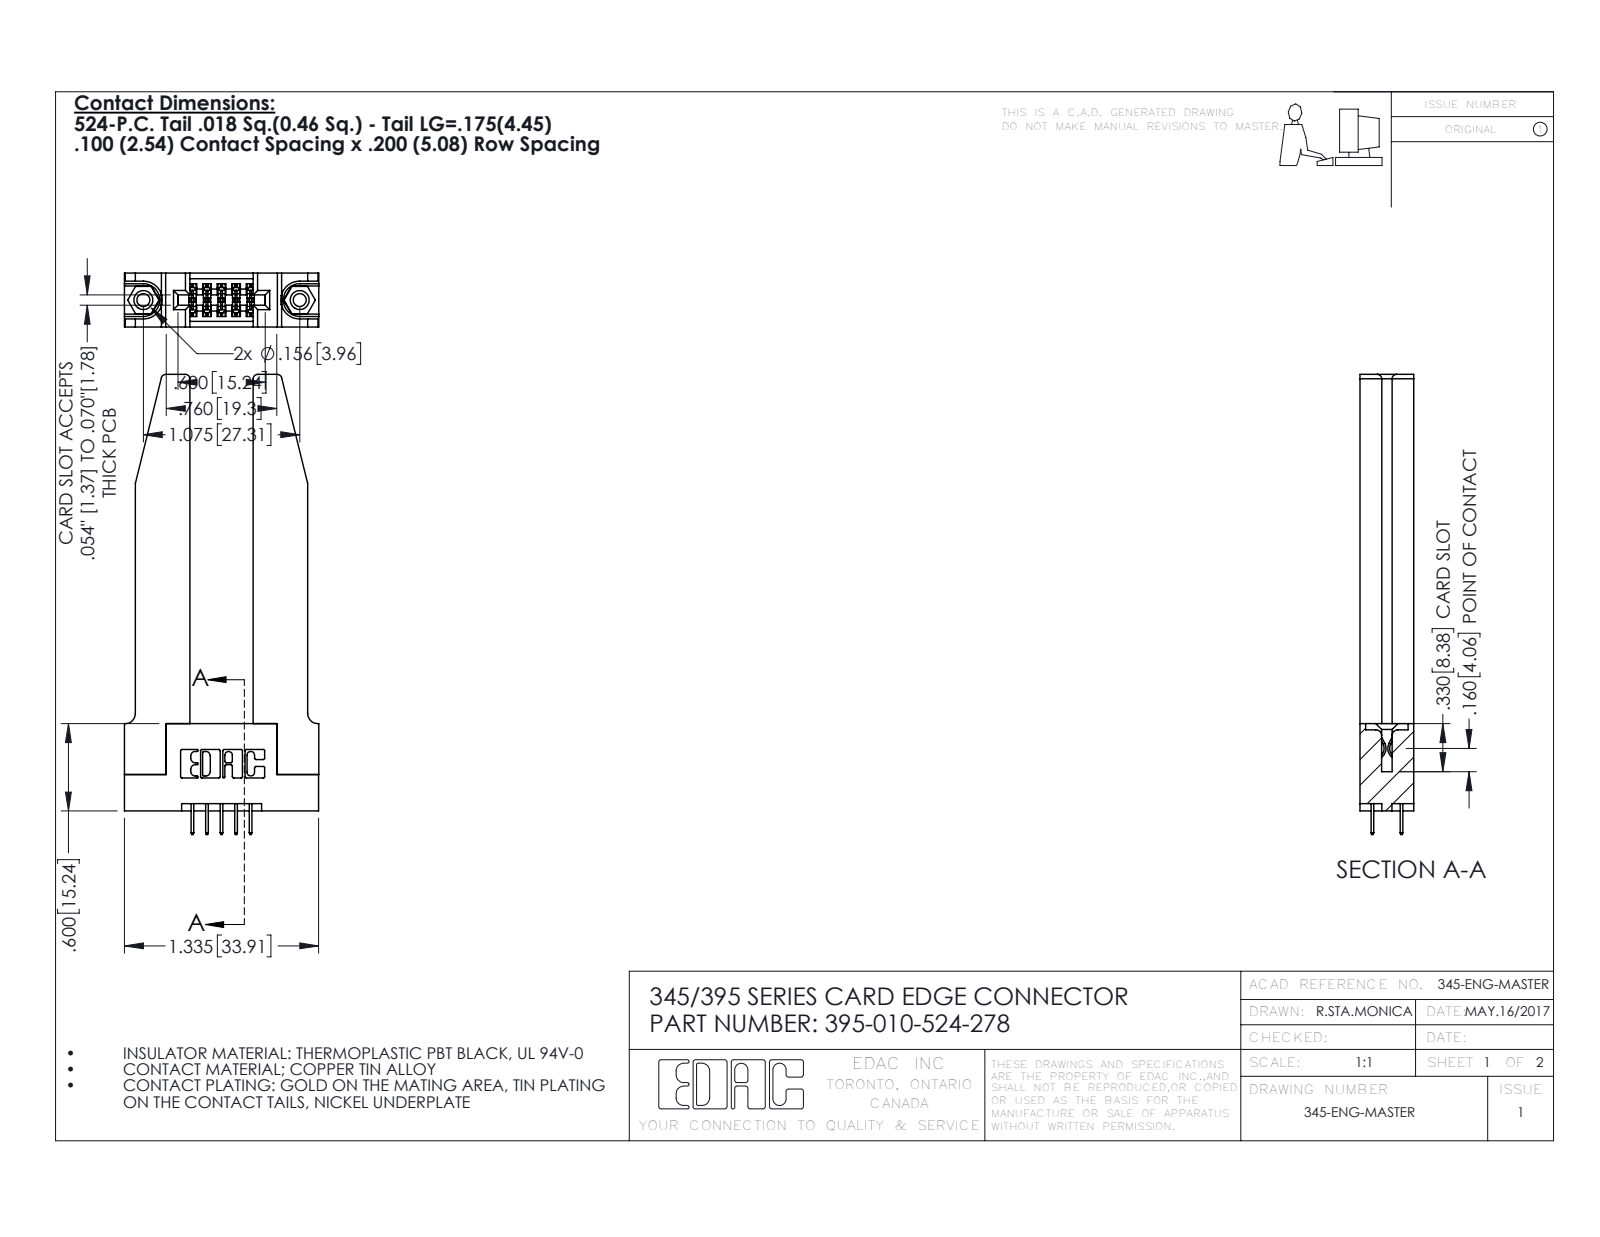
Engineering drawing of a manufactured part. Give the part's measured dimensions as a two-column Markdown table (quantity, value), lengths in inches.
| quantity | value |
| --- | --- |
| part name | 345-292-001_345-293-124; 345-220-078_345-220-078; 345 Part_Flush Mounting Lugs - 0.156 Dia-TH; 395-010-524-278 (+1 more) |
| STEP written by | SolidWorks 2016 (CONFIG_CONTROL_DESIGN) |
| units | inches |
| bodies | 15 solids, 900 faces (612 planar, 236 cylindrical, 52 other) |
| overall size | 3.162 × 1.336 × 0.37 |
| volume | 0.653 in³ |
| surface area | 16.16 in² |
| round holes (diameter × count) | 0.089 × 2, 0.125 × 2, 0.156 × 2, 0.064 × 1 |
| round bosses / shafts (diameter × count) | 0.155 × 2 |
| partial cylindrical surfaces (radius × count) | 0.01 × 22, 0.006 × 15, 0.03 × 8, 0.007 × 6, 0.031 × 6, 0.026 × 3, 0.014 × 2, 0.019 × 2 |
| main face-to-face distances | 0.37, 0.15, 0.22, 0.435, 0.072, 0.148, 0.077, 0.298, 0.2, 0.095 |
| hole center spacings | 0.27, 0.847, 1.075 |
